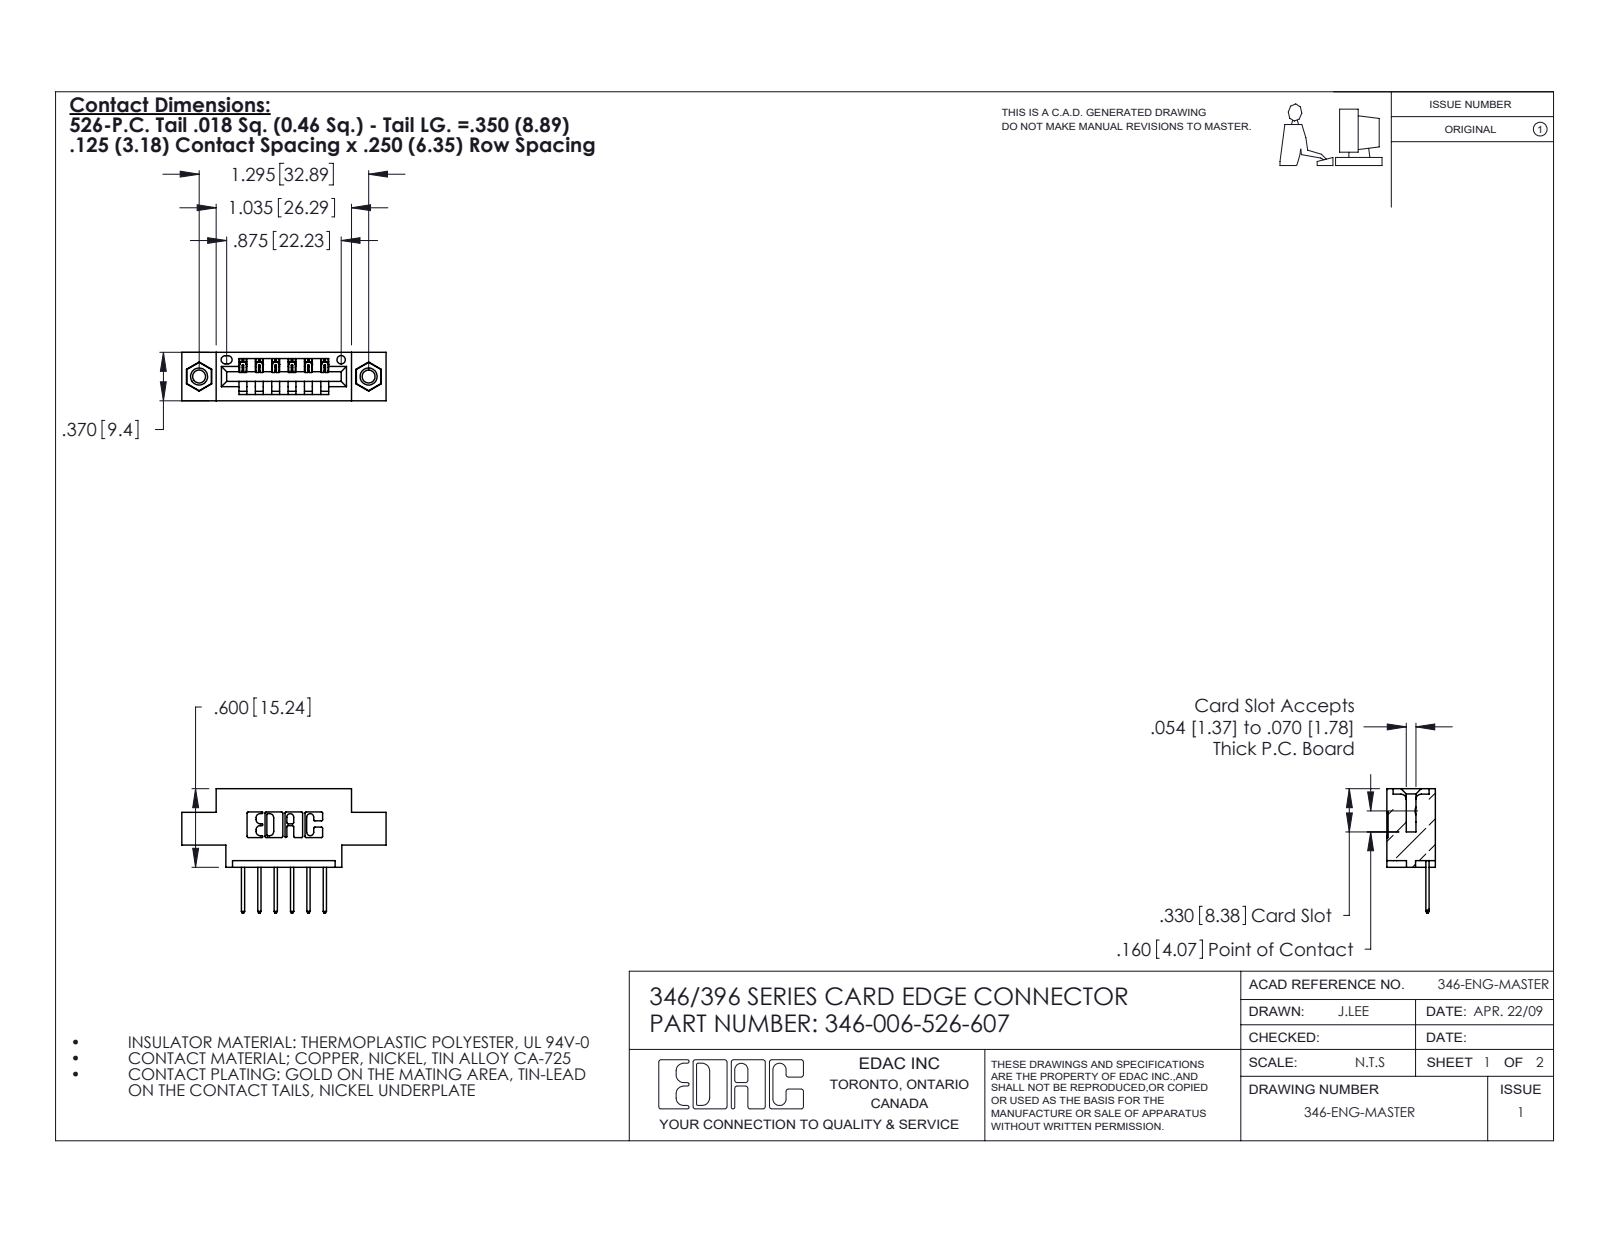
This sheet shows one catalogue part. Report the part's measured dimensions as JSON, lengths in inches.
{"part_name": "346 Part_0.170 Offset - 0.156 Dia-TI; 345-292-001_345-293-126; 345-250-001_345-250-005-103; 346-006-526-607", "step_written_by": "SolidWorks 2020 (CONFIG_CONTROL_DESIGN)", "units": "inches", "bodies": {"solids": 9, "faces": 534, "planar": 352, "cylindrical": 166, "other": 16}, "overall_size": [1.56, 0.95, 0.37], "volume_in3": 0.206, "surface_area_in2": 6.224, "round_holes": [[0.098, 2], [0.125, 2], [0.156, 2], [0.064, 1]], "round_bosses_or_shafts": [[0.155, 2]], "partial_cylinders_radius": [[0.01, 22], [0.006, 12], [0.01, 12], [0.007, 6], [0.031, 6], [0.026, 3], [0.031, 2], [0.04, 2]], "face_to_face_distances": [0.25, 0.37, 0.048, 0.322, 0.222, 0.148, 0.1, 0.174, 0.072, 0.298], "hole_center_spacings": [0.246, 1.092, 1.295]}
